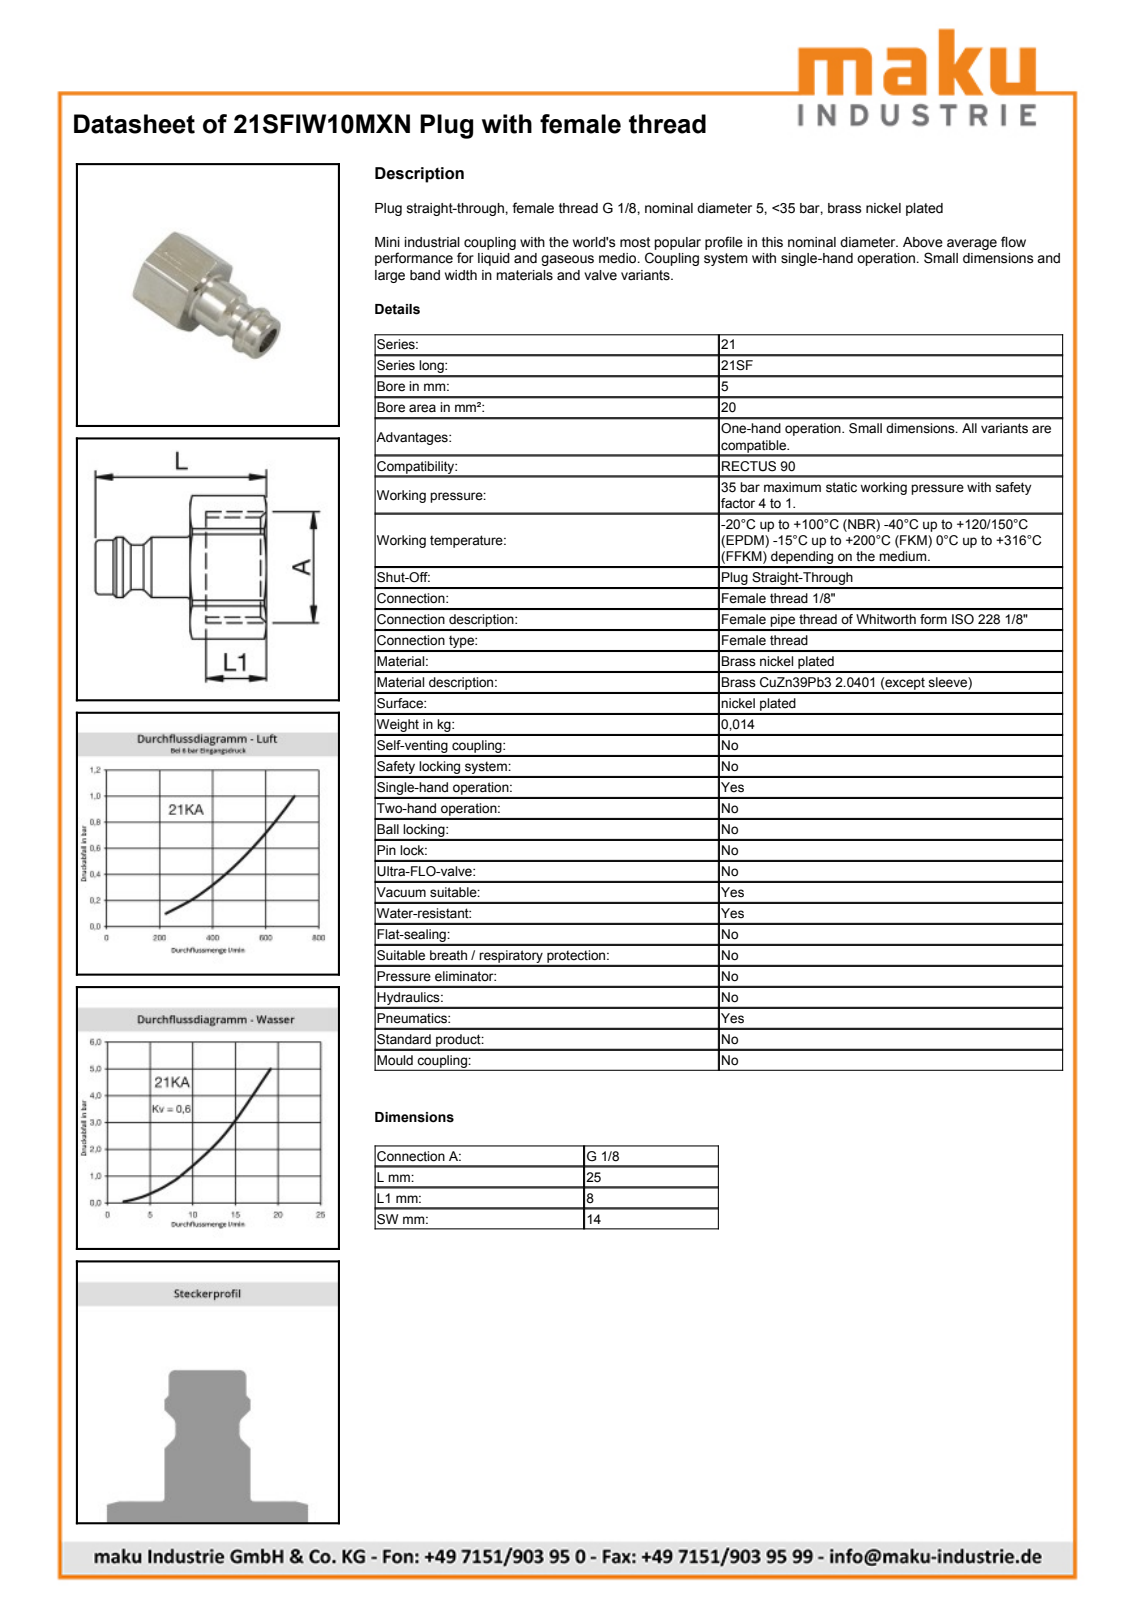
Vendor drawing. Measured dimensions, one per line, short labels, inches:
name: D109906
written by: Autodesk Inventor 2013 (AUTOMOTIVE_DESIGN)
unit: in
bodies: 1 solid, 42 faces (10 planar, 12 cylindrical, 20 other)
size: 0.965 × 0.622 × 0.551
volume: 0.098 in³; area: 2.561 in²
holes: 1× ⌀0.195, 1× ⌀0.383
bosses: 1× ⌀0.354, 1× ⌀0.319, 1× ⌀0.262
rounds: 1× R0.311
face distances: 0.551, 0.409, 0.094, 0.315, 0.555, 0.65, 0.965
